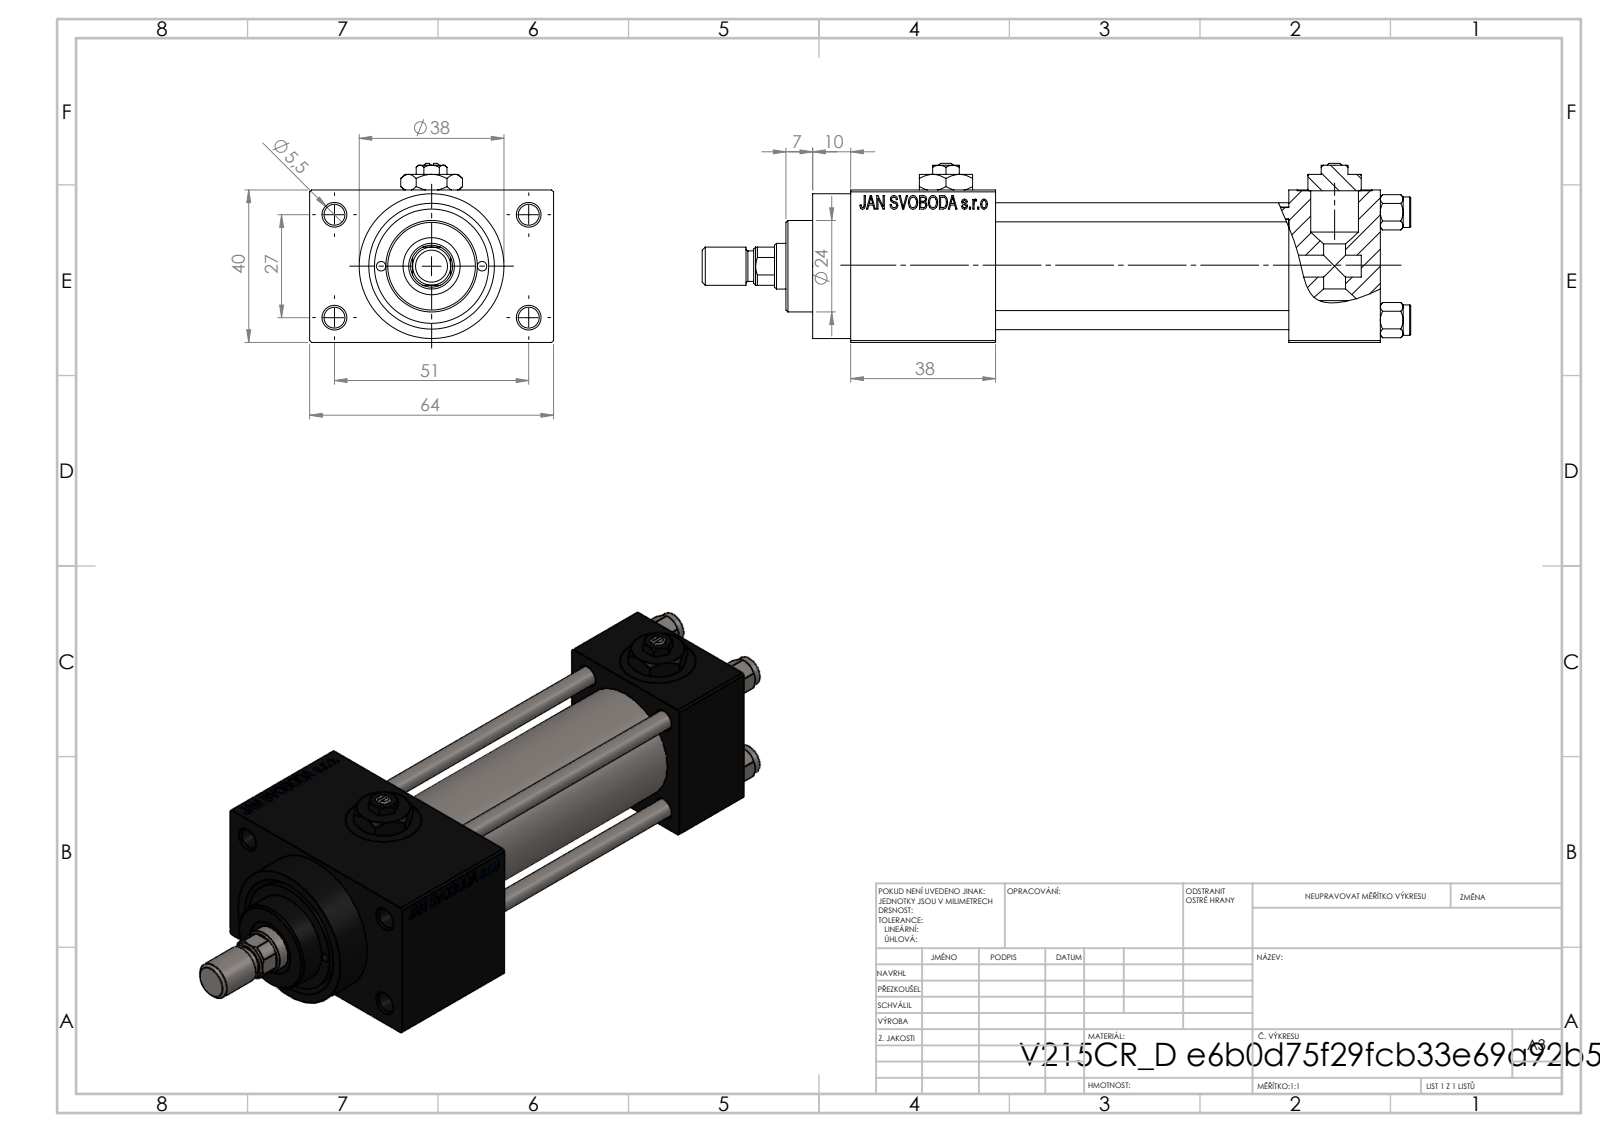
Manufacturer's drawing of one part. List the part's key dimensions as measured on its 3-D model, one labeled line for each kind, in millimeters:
Part name (STEP PRODUCT): NUT_M5_D; V215_VC_A; V215CR_D_Body; ROD_END_AH (+3 more)
STEP written by: SolidWorks 2019 (CONFIG_CONTROL_DESIGN)
Units: millimetres
Bodies: 14 solids, 1224 faces (548 planar, 108 cylindrical, 568 other)
Overall size (bounding box): 186 × 64 × 47
Volume: 188 752 mm³ · Surface area: 72 218 mm²
Round holes (diameter × count): ⌀5 ×4, ⌀5.5 ×4, ⌀20 ×3, ⌀2.5 ×2, ⌀7 ×2, ⌀13.16 ×2, ⌀6.5 ×1, ⌀12 ×1, ⌀15 ×1, ⌀25 ×1, ⌀30 ×1
Round bosses / shafts (diameter × count): ⌀8 ×5, ⌀38 ×1, ⌀31 ×1, ⌀24 ×1, ⌀10 ×1
Partial cylindrical surfaces — rounded edges, fillets, slot ends (radius × count): R5.5 ×1
Main face-to-face distances: 40, 12, 52, 77, 24, 101, 64, 38, 115, 139
Hole centre spacings: 11.37, 14.18, 18.23, 20.01, 28.3, 28.85, 29.89, 30.84
